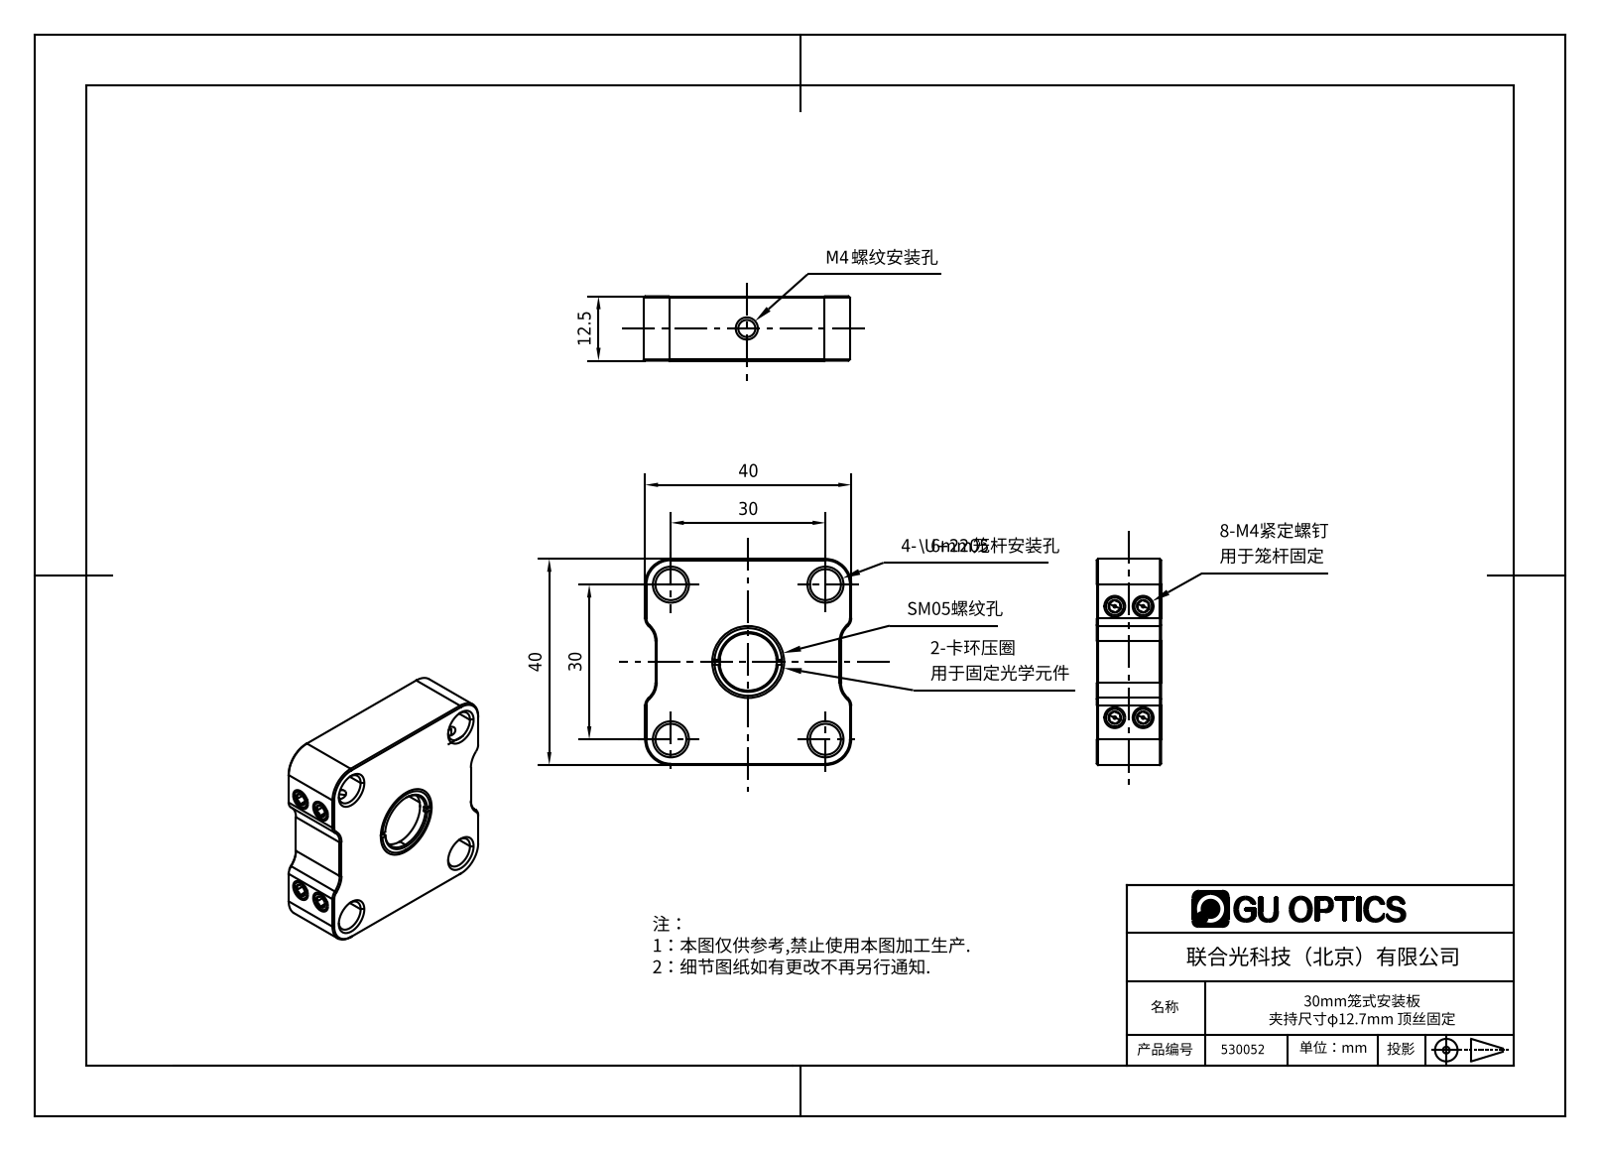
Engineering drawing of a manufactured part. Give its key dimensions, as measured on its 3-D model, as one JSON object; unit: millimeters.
{"part_name": "2.2.1.28_L30B-SM05H_30 mm笼板，用于0.5英寸光学元件，厚度0.5英寸，附带2个SM05卡环，M4螺纹", "step_written_by": "SolidWorks 2018 (AUTOMOTIVE_DESIGN)", "units": "millimeters", "bodies": {"solids": 0, "faces": 324, "planar": 106, "cylindrical": 44, "other": 174}, "overall_size": [40, 40, 12.5], "round_holes": [[3.3, 5], [6, 4], [11.09, 1], [11.09, 1], [12.95, 1]], "partial_cylinders_radius": [[2, 4], [4, 4], [5, 4]], "face_to_face_distances": [12.5, 40, 2, 38, 36, 2.1, 36.76, 3.35, 5.45, 17.15], "hole_center_spacings": [21.21, 30, 5.5, 21.6, 22.29, 42.43]}
